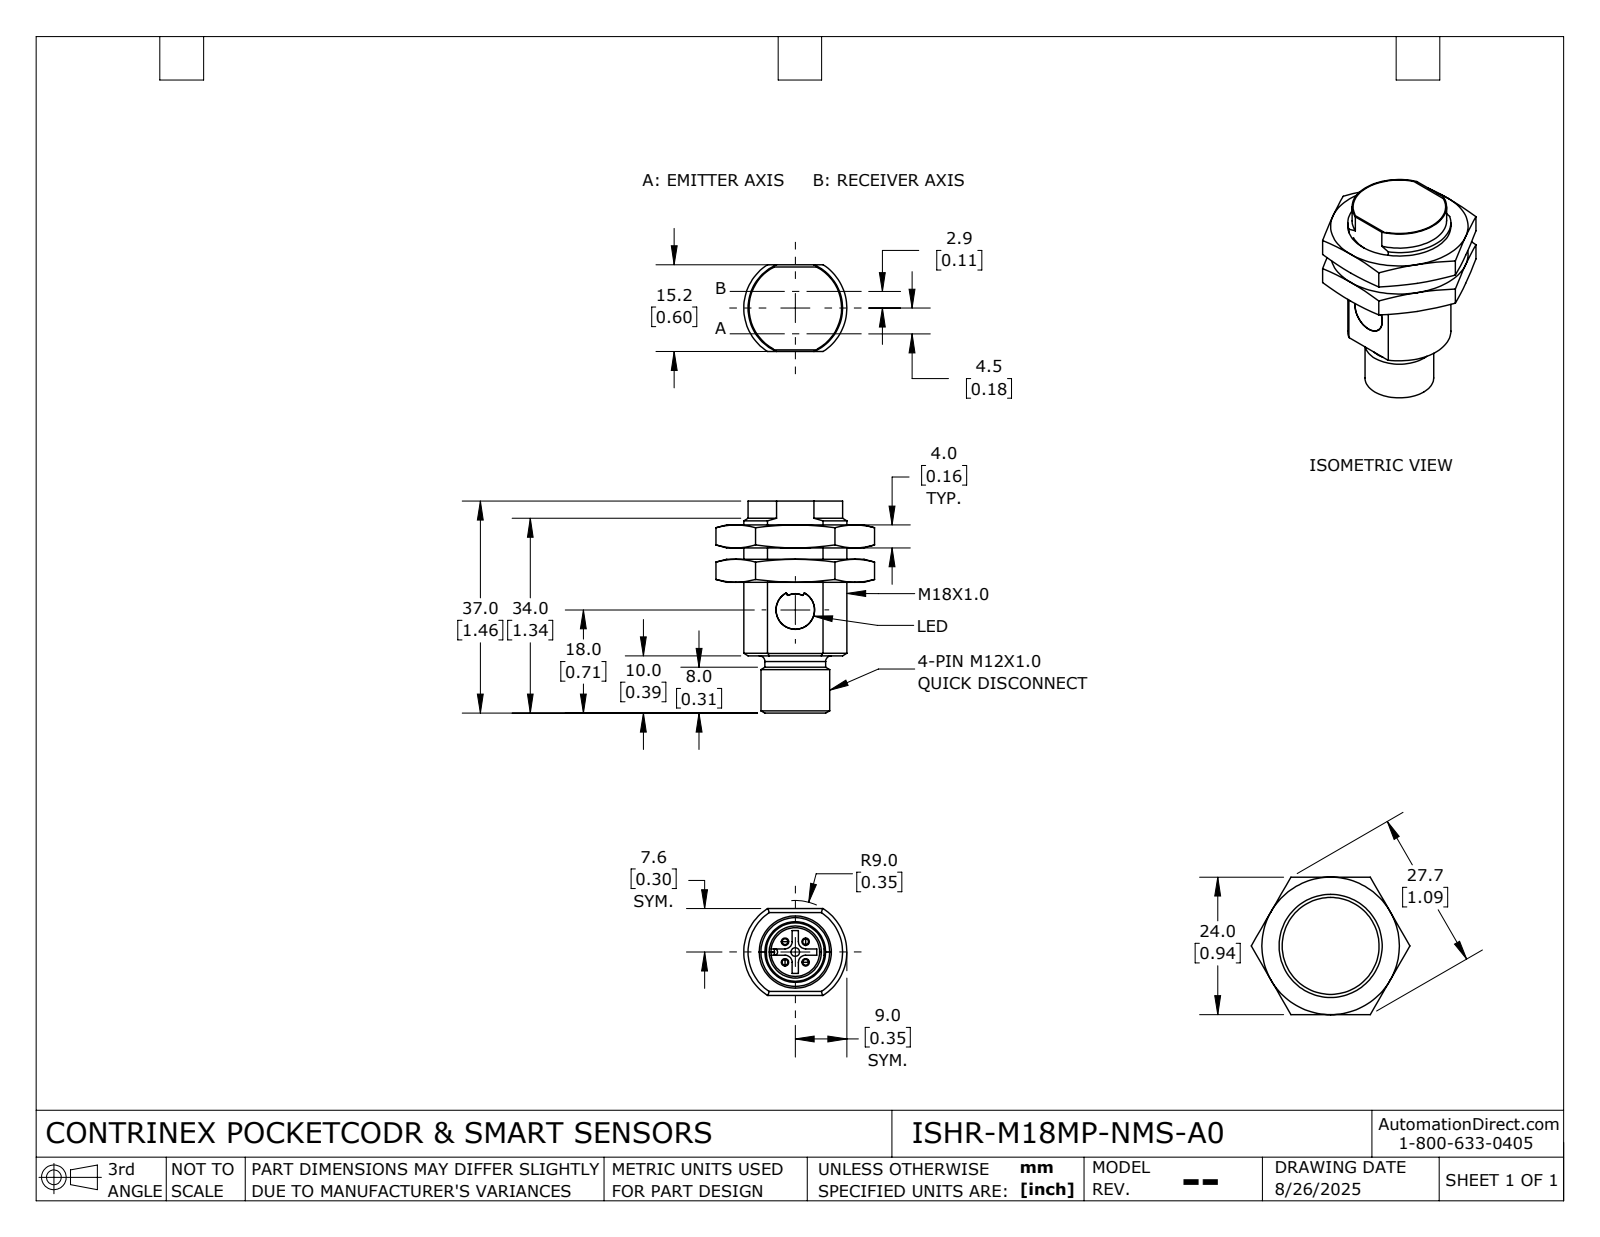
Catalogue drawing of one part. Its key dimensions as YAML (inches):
part_name: "ISHR-M18MP-NMS-A0"
step_written_by: "SolidWorks 2024 (AUTOMOTIVE_DESIGN)"
units: inches
bodies: {solids: 3, faces: 157, planar: 67, cylindrical: 41, other: 49}
overall_size: [1.457, 1.091, 0.945]
volume: 0.549
surface_area: 7.341
round_holes:
  - {diameter: 0.059, count: 1}
  - {diameter: 0.266, count: 1}
  - {diameter: 0.335, count: 1}
  - {diameter: 0.666, count: 1}
round_bosses_or_shafts:
  - {diameter: 0.039, count: 4}
  - {diameter: 0.472, count: 1}
  - {diameter: 0.417, count: 1}
  - {diameter: 0.264, count: 1}
partial_cylinders:
  - {radius: 0.004, count: 4}
  - {radius: 0.049, count: 4}
  - {radius: 0.005, count: 2}
  - {radius: 0.02, count: 2}
  - {radius: 0.022, count: 1}
  - {radius: 0.111, count: 1}
  - {radius: 0.112, count: 1}
  - {radius: 0.325, count: 1}
face_to_face_distances: [0.236, 0.157, 0.945, 0.597, 0.394, 0.174, 0.771, 0.4, 0.164, 0.557]
